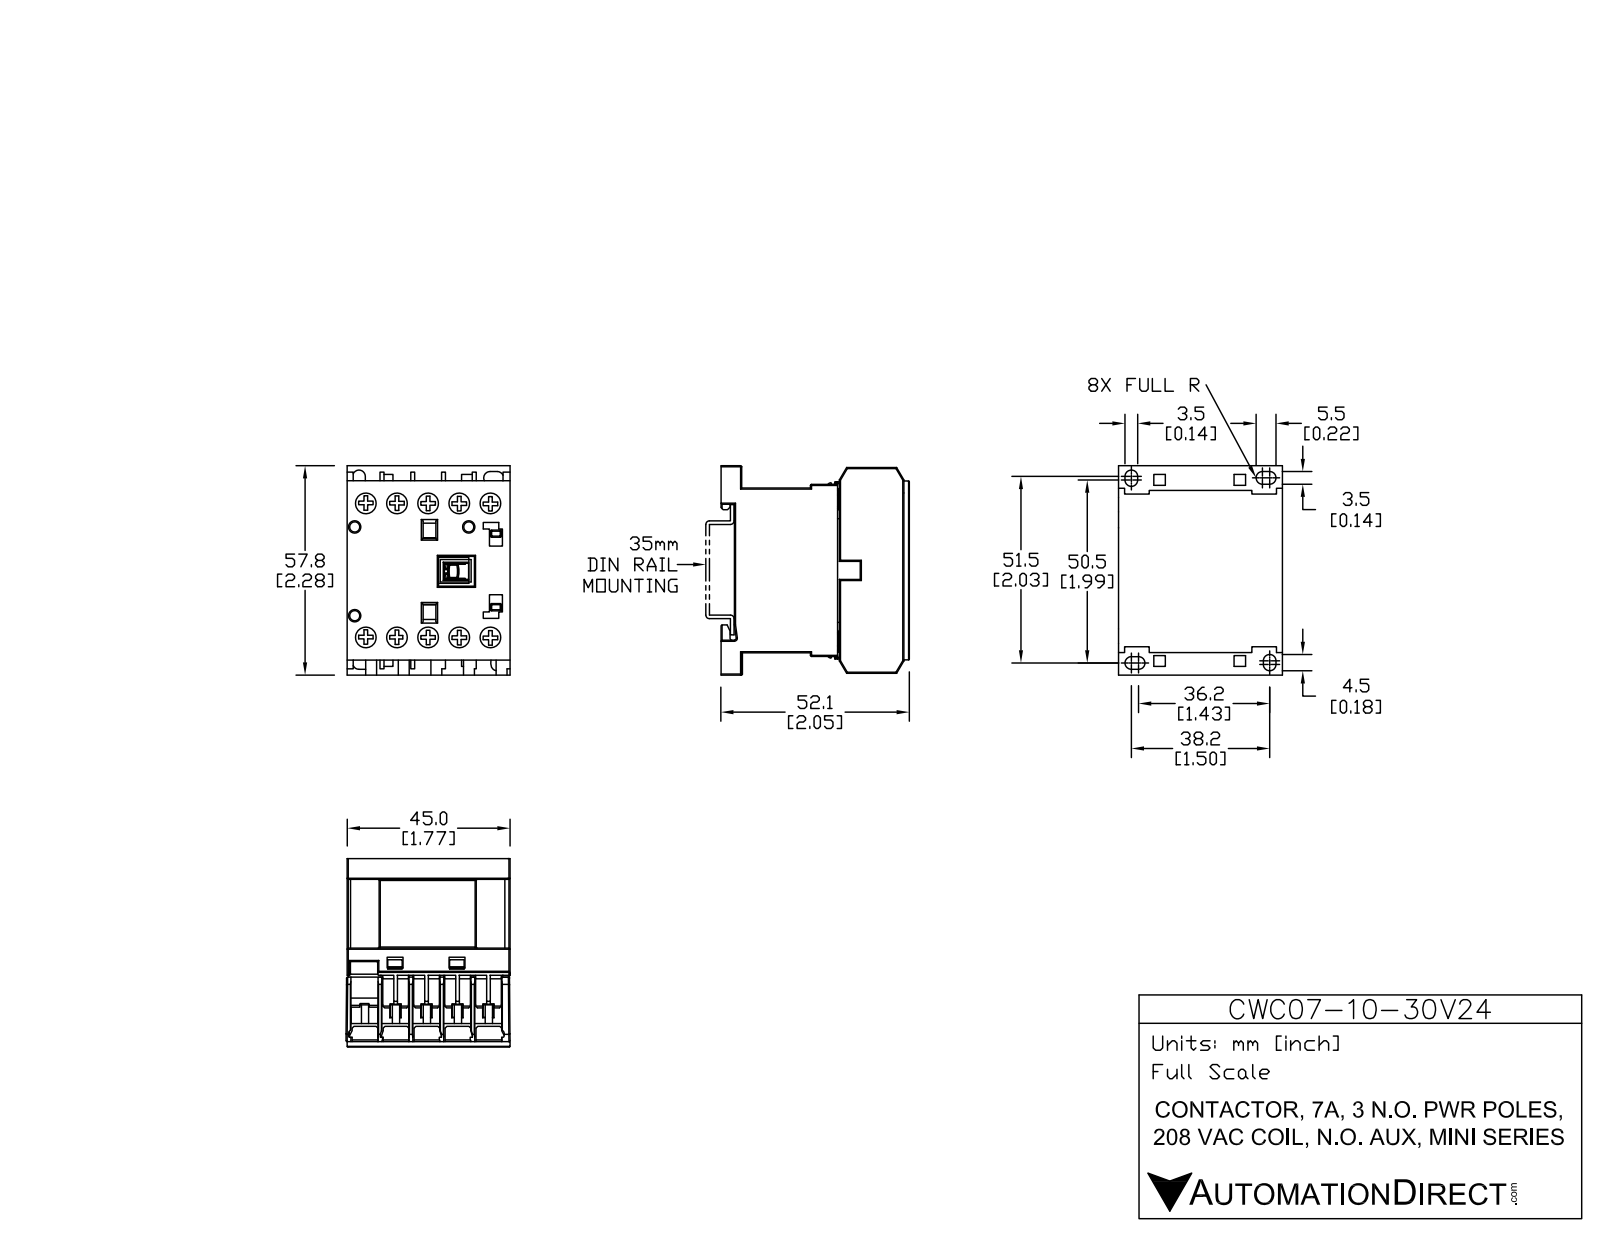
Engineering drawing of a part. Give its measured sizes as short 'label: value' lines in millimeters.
name: CWC07-10-30V24
written by: SolidWorks 2013 (AUTOMOTIVE_DESIGN)
unit: mm
bodies: 15 solids, 535 faces (445 planar, 90 cylindrical, 0 other)
size: 58.04 × 52.12 × 45.75
volume: 97 133 mm³; area: 30 437 mm²
holes: 10× ⌀6.2, 3× ⌀2.8
bosses: 10× ⌀5.9
rounds: 20× R0.3, 6× R1.72, 2× R1.73, 1× R0.32, 1× R0.42, 1× R0.55
face distances: 8.25, 45.5, 1.25, 16.5, 9.5, 5.5, 17.75, 5.13, 10.63, 7
hole spacings: 8.55, 37.94, 17.1, 40.72, 36.96, 25.65, 44.99, 6.91
